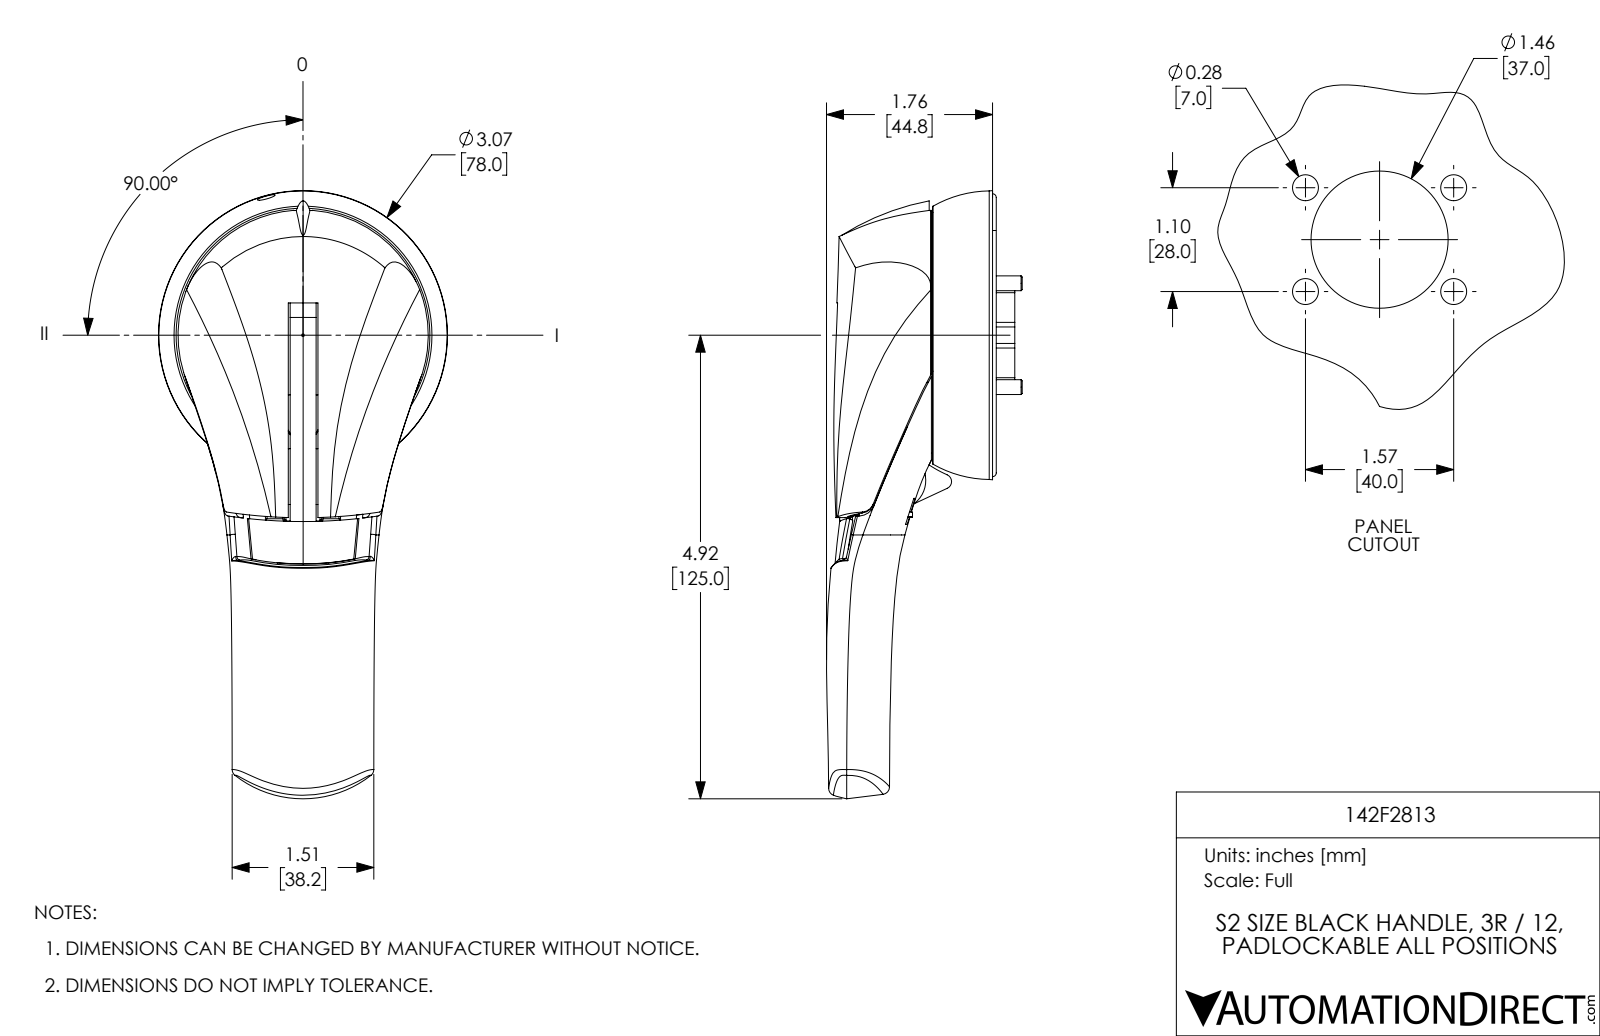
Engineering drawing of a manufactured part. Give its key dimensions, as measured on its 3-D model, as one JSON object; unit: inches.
{"part_name": "142F2813", "step_written_by": "SolidWorks 2017 (AUTOMOTIVE_DESIGN)", "units": "inches", "bodies": {"solids": 8, "faces": 1516, "planar": 810, "cylindrical": 548, "other": 158}, "overall_size": [6.458, 3.07, 2.079], "volume_in3": 9.514, "surface_area_in2": 87.31, "round_holes": [[0.157, 6], [0.339, 4], [0.425, 4], [0.03, 3], [0.169, 2], [0.362, 2], [0.118, 1], [0.189, 1], [2.992, 1]], "round_bosses_or_shafts": [[0.02, 11], [0.335, 4], [0.315, 4], [0.089, 3], [0.069, 3], [0.228, 2], [2.819, 1], [2.701, 1]], "partial_cylinders_radius": [[0.01, 221], [0.015, 20], [0.034, 20], [0.03, 15], [0.039, 4], [0.025, 3], [5.437, 3], [0.079, 2]], "face_to_face_distances": [0.024, 0.701, 0.713, 0.689, 0.035, 0.102, 0.276, 0.173, 0.244, 0.047], "hole_center_spacings": [0.961, 0.309, 0.669, 1.098, 1.102, 1.203, 1.575, 1.881]}
